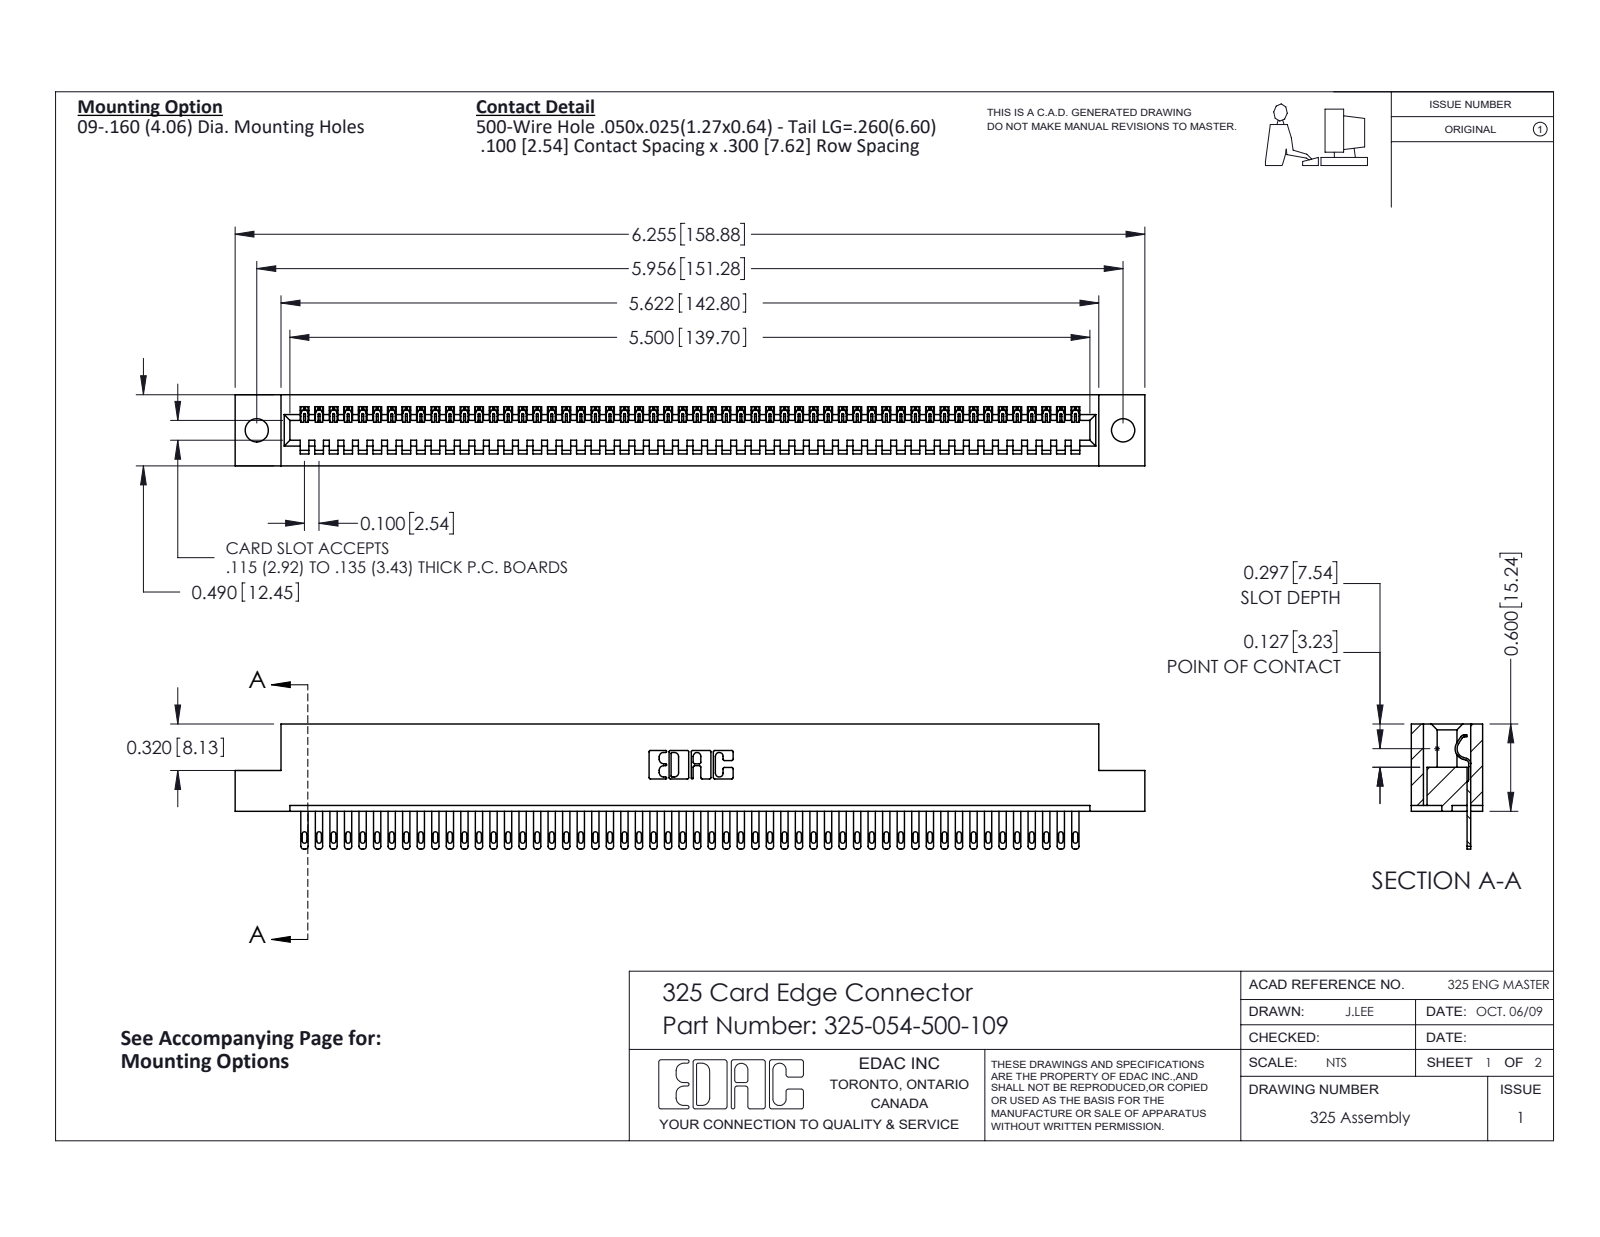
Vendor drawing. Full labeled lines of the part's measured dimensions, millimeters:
Part name (STEP PRODUCT): 325 Part_.160 TH; 325-054-500-109; 325-292-001_325-293-100
STEP written by: SolidWorks 2016 (CONFIG_CONTROL_DESIGN)
Units: millimetres
Bodies: 55 solids, 3030 faces (2014 planar, 1016 cylindrical, 0 other)
Overall size (bounding box): 158.9 × 21.8 × 12.4
Volume: 20 070 mm³ · Surface area: 22 150 mm²
Round holes (diameter × count): ⌀4.1 ×2
Partial cylindrical surfaces — rounded edges, fillets, slot ends (radius × count): R0.2 ×108, R0.4 ×108, R0.5 ×108, R0.3 ×22, R0.2 ×6, R0.8 ×6, R0.7 ×3, R0.4 ×1
Main face-to-face distances: 2.1, 10.3, 7.6, 12.4, 2.7, 9.7, 0.6, 8.3, 14.2, 6.7
Hole centre spacings: 151.3
